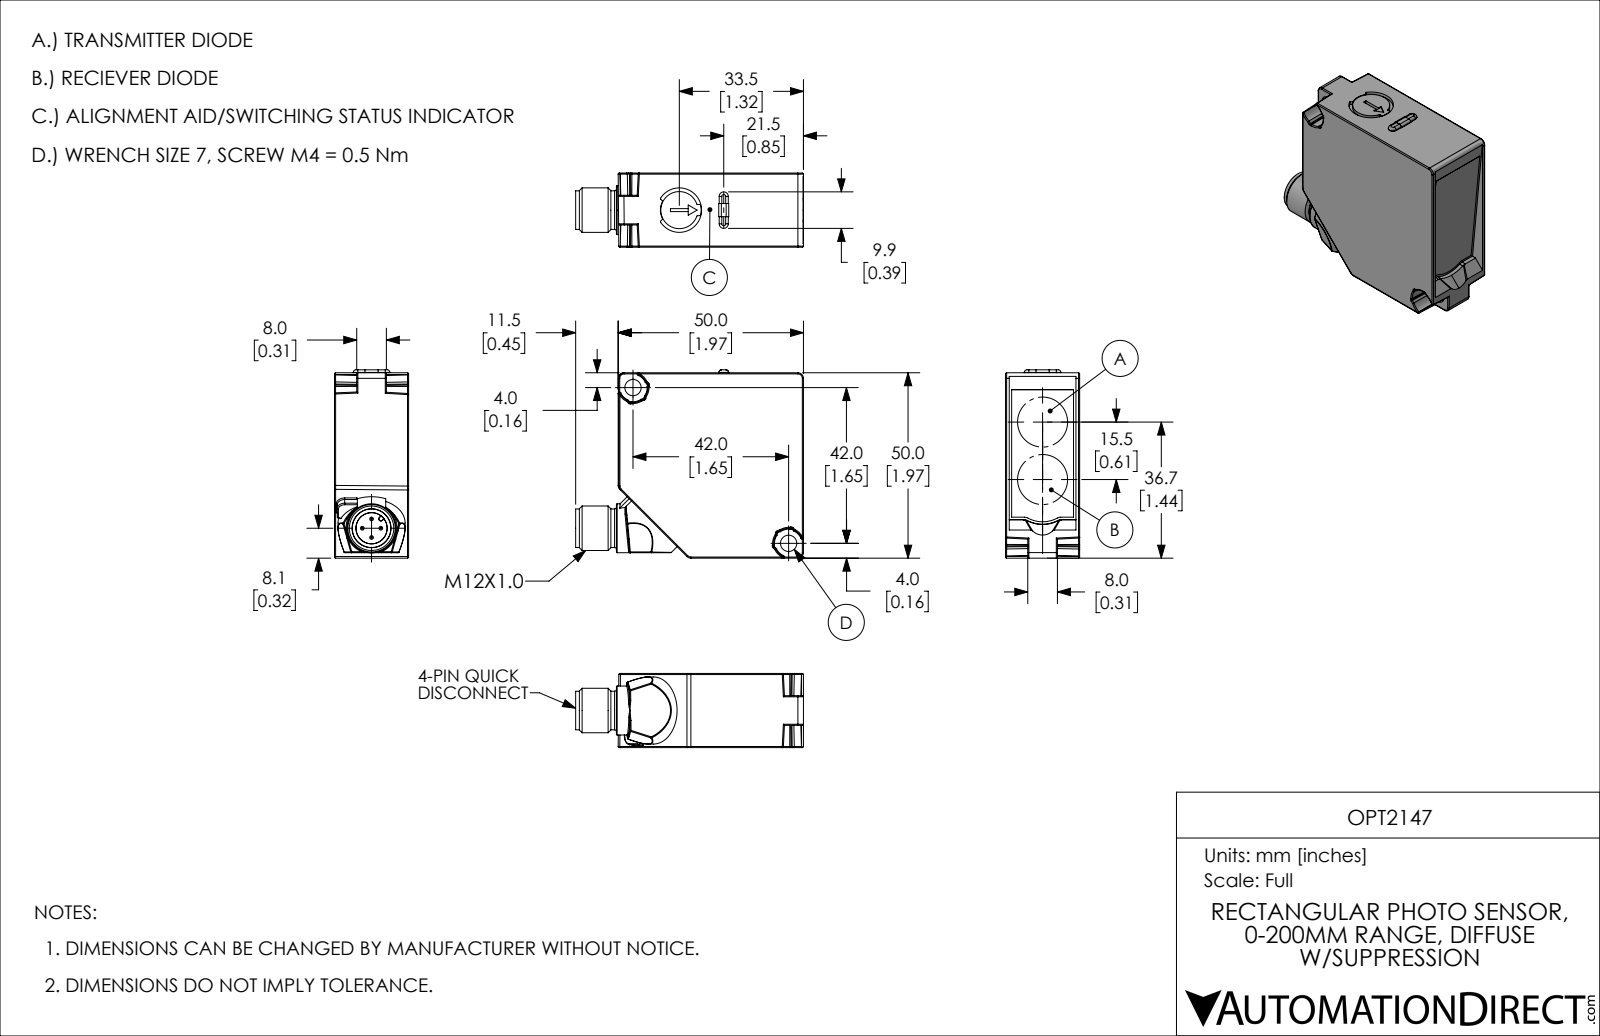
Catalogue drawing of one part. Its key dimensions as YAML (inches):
part_name: "OPT2147"
step_written_by: "SolidWorks 2019 (AUTOMOTIVE_DESIGN)"
units: inches
bodies: {solids: 1, faces: 342, planar: 109, cylindrical: 120, other: 113}
overall_size: [2.42, 2, 0.787]
volume: 2.816
surface_area: 15.64
round_holes:
  - {diameter: 0.173, count: 2}
  - {diameter: 0.472, count: 1}
  - {diameter: 0.713, count: 1}
round_bosses_or_shafts:
  - {diameter: 0.039, count: 4}
  - {diameter: 0.52, count: 1}
  - {diameter: 0.472, count: 1}
  - {diameter: 0.409, count: 1}
  - {diameter: 0.394, count: 1}
partial_cylinders:
  - {radius: 0.012, count: 64}
  - {radius: 0.008, count: 8}
  - {radius: 0.059, count: 5}
  - {radius: 0.079, count: 5}
  - {radius: 0.028, count: 4}
  - {radius: 0.048, count: 2}
  - {radius: 0.201, count: 1}
  - {radius: 0.232, count: 1}
face_to_face_distances: [0.787, 1.969, 0.039, 0.748, 0.236, 0.551, 0.197, 0.512, 0.058, 1.911]
hole_center_spacings: [2.339]
